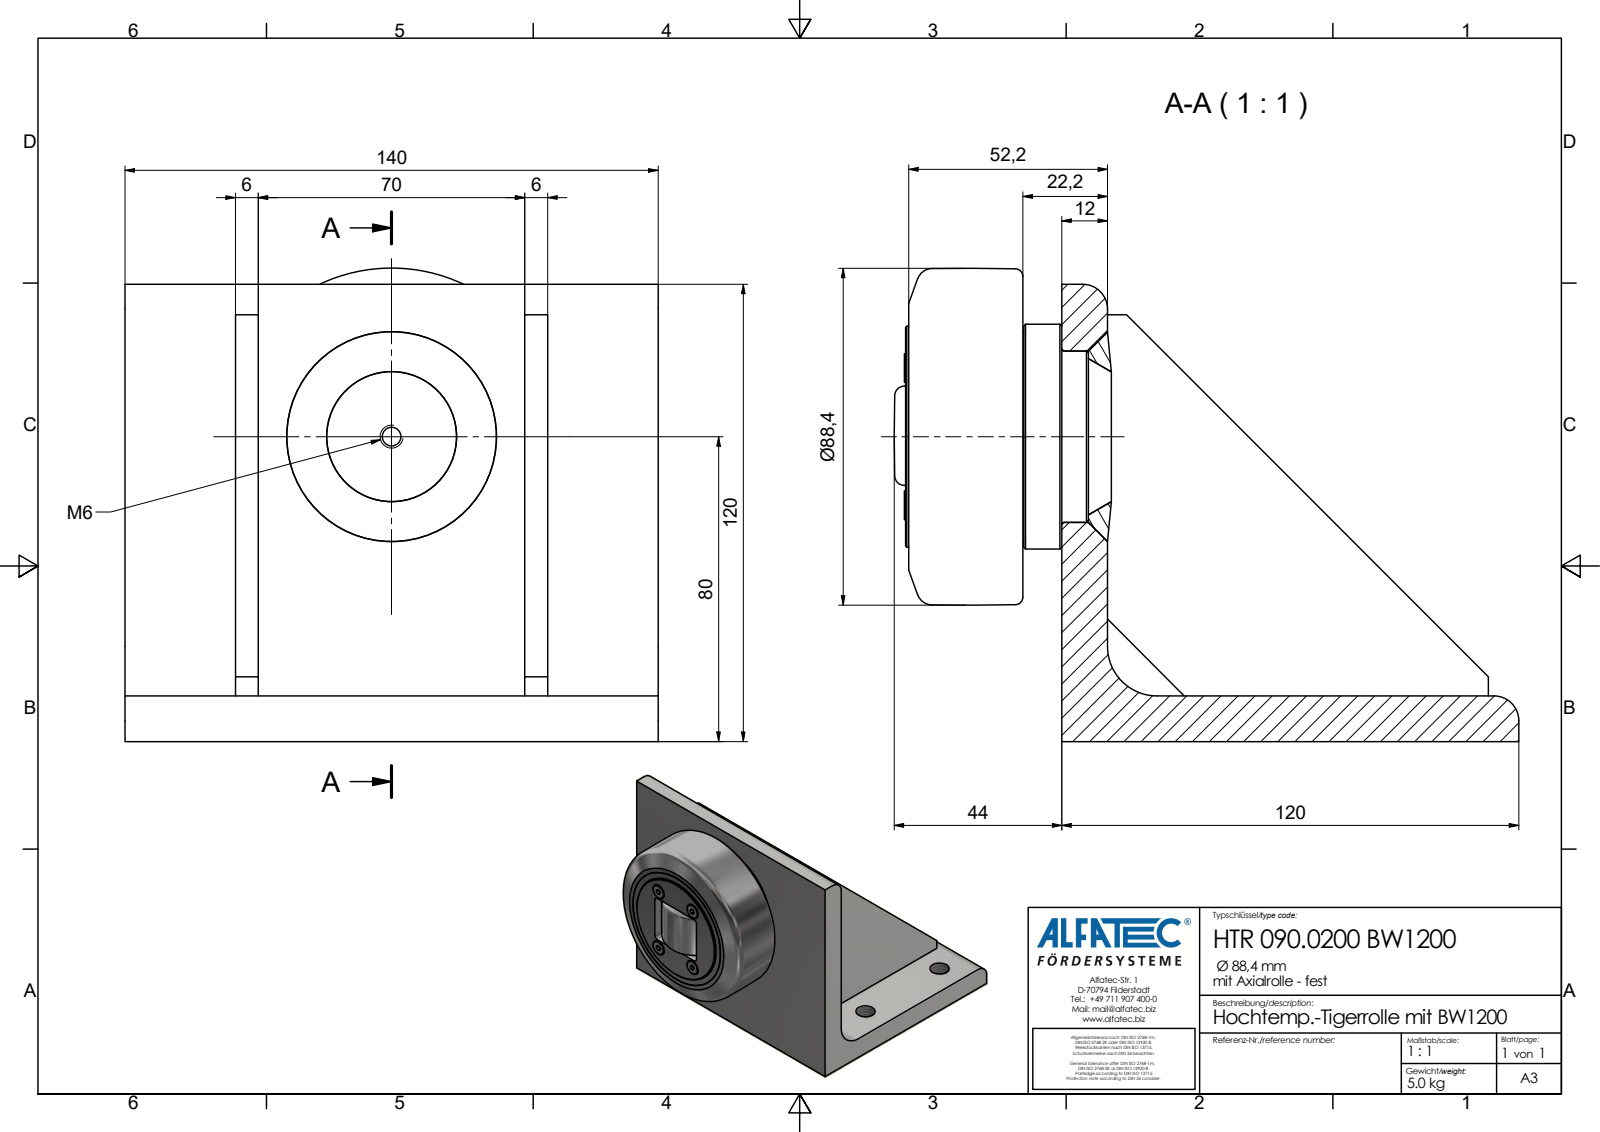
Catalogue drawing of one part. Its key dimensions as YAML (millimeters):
part_name: "HTR 090.0200 BW1200_Kontur"
step_written_by: "Autodesk Inventor 2020 (AP242_MANAGED_MODEL_BASED_3D_ENGINEERING_MIM_LF)"
units: millimeters
bodies: {solids: 1, faces: 104, planar: 67, cylindrical: 22, other: 15}
overall_size: [164, 140, 124.2]
volume: 656278
surface_area: 110612
round_holes:
  - {diameter: 10.11, count: 4}
  - {diameter: 2.5, count: 1}
  - {diameter: 4.92, count: 1}
round_bosses_or_shafts:
  - {diameter: 7.53, count: 4}
  - {diameter: 59, count: 1}
  - {diameter: 58, count: 1}
  - {diameter: 55.3, count: 1}
partial_cylinders:
  - {radius: 2, count: 4}
  - {radius: 6.5, count: 2}
  - {radius: 1.5, count: 1}
  - {radius: 13, count: 1}
  - {radius: 25, count: 1}
face_to_face_distances: [12, 76, 6, 29, 35, 105, 111, 82, 70, 10.2]
hole_center_spacings: [55, 110, 122.98]
